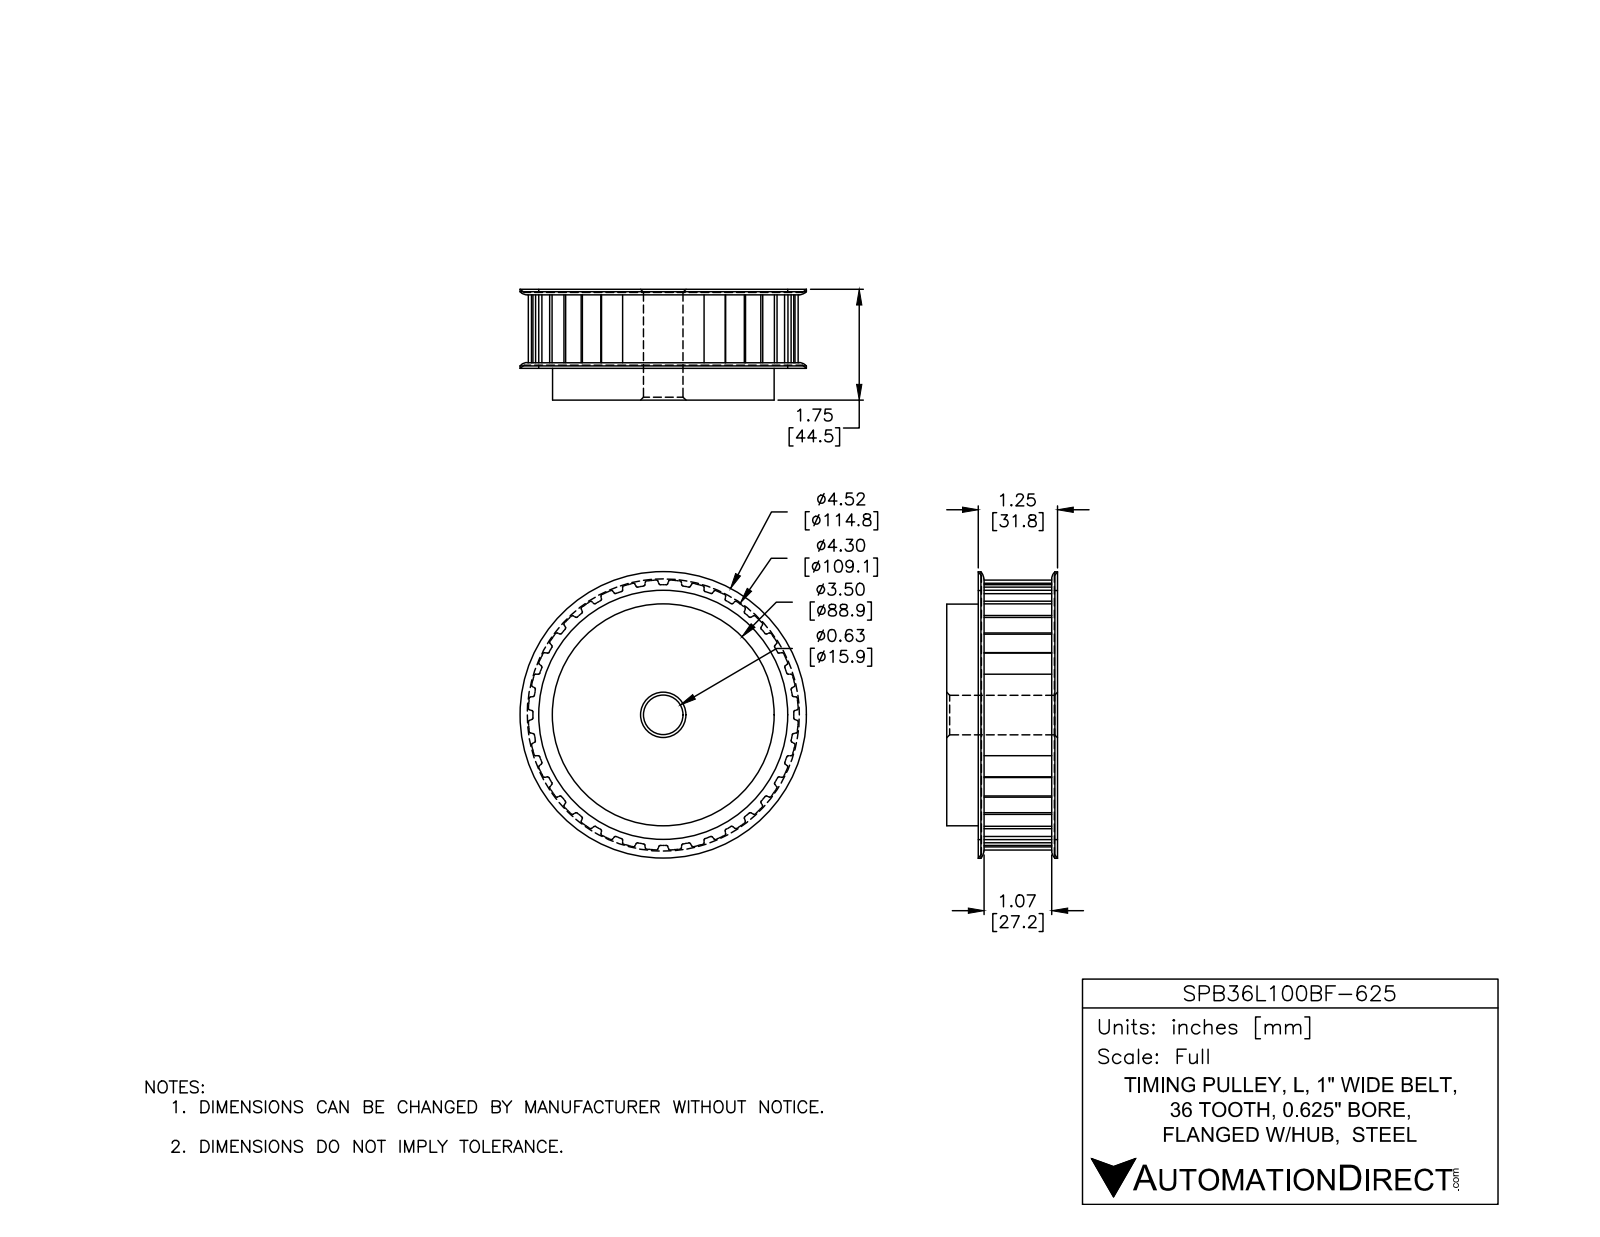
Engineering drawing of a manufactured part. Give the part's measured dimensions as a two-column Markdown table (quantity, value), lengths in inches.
| quantity | value |
| --- | --- |
| part name | SPB36L100BF-625 |
| STEP written by | SolidWorks 2015 (AUTOMOTIVE_DESIGN) |
| units | inches |
| bodies | 1 solid, 335 faces (150 planar, 169 cylindrical, 16 other) |
| overall size | 4.52 × 4.52 × 1.75 |
| volume | 21.65 in³ |
| surface area | 65.43 in² |
| round holes (diameter × count) | 0.625 × 1 |
| round bosses / shafts (diameter × count) | 4.52 × 1, 3.932 × 1, 3.5 × 1 |
| partial cylindrical surfaces (radius × count) | 0.02 × 126, 2.134 × 1 |
| main face-to-face distances | 1.75, 0.05, 1.2, 1.15, 1.7, 0.55, 1.25, 0.5, 4.266, 2.703 |
